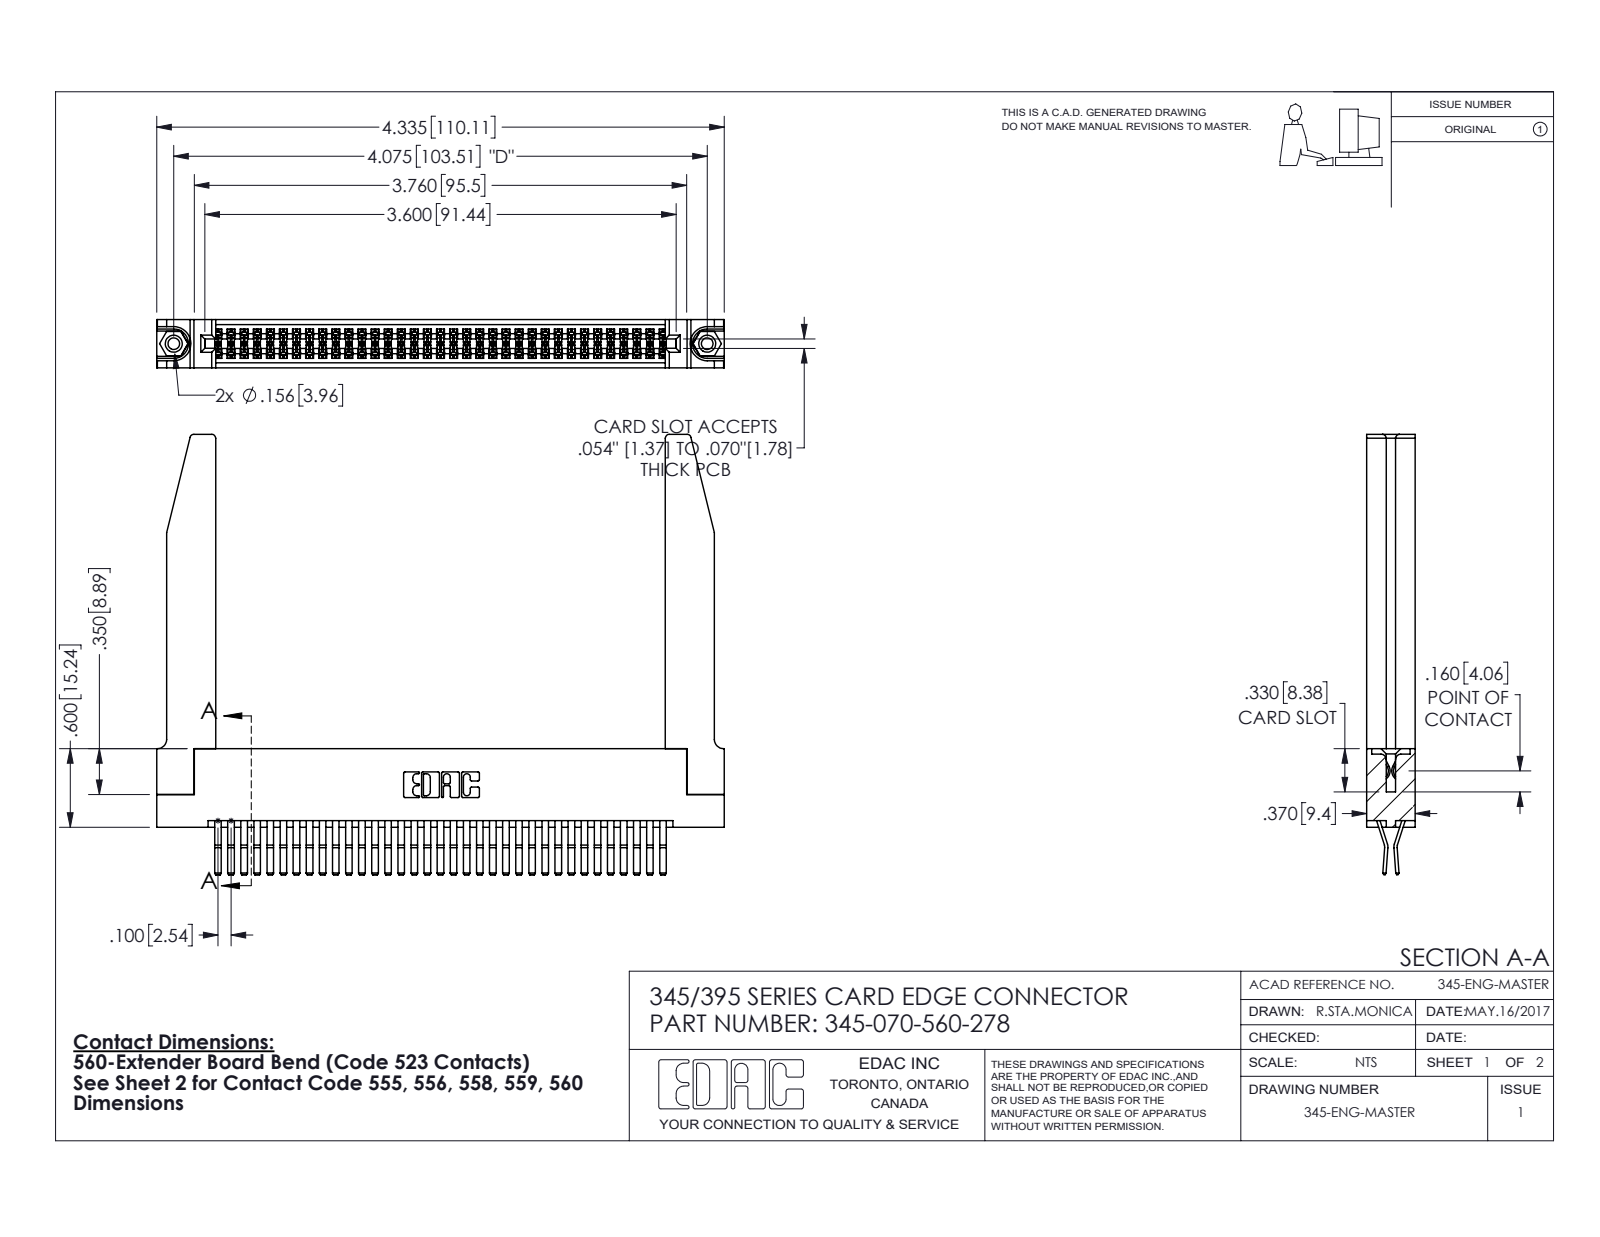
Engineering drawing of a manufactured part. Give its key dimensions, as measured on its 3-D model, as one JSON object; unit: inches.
{"part_name": "345-292-001_560 Tail; 345-070-560-278; 345-220-078_345-220-078; 345-250-001_345-250-001-102 (+1 more)", "step_written_by": "SolidWorks 2016 (CONFIG_CONTROL_DESIGN)", "units": "inches", "bodies": {"solids": 75, "faces": 4000, "planar": 2532, "cylindrical": 1416, "other": 52}, "overall_size": [4.336, 3.362, 0.37], "volume_in3": 1.151, "surface_area_in2": 37.63, "round_holes": [[0.089, 2], [0.125, 2], [0.156, 2], [0.064, 1]], "round_bosses_or_shafts": [[0.155, 2]], "partial_cylinders_radius": [[0.006, 106], [0.01, 22], [0.03, 8], [0.007, 6], [0.031, 6], [0.026, 3], [0.01, 2], [0.014, 2]], "face_to_face_distances": [0.37, 0.072, 0.298, 0.025, 0.2, 0.098, 0.272, 0.225, 0.148, 0.15], "hole_center_spacings": [0.27, 3.839, 4.075]}
